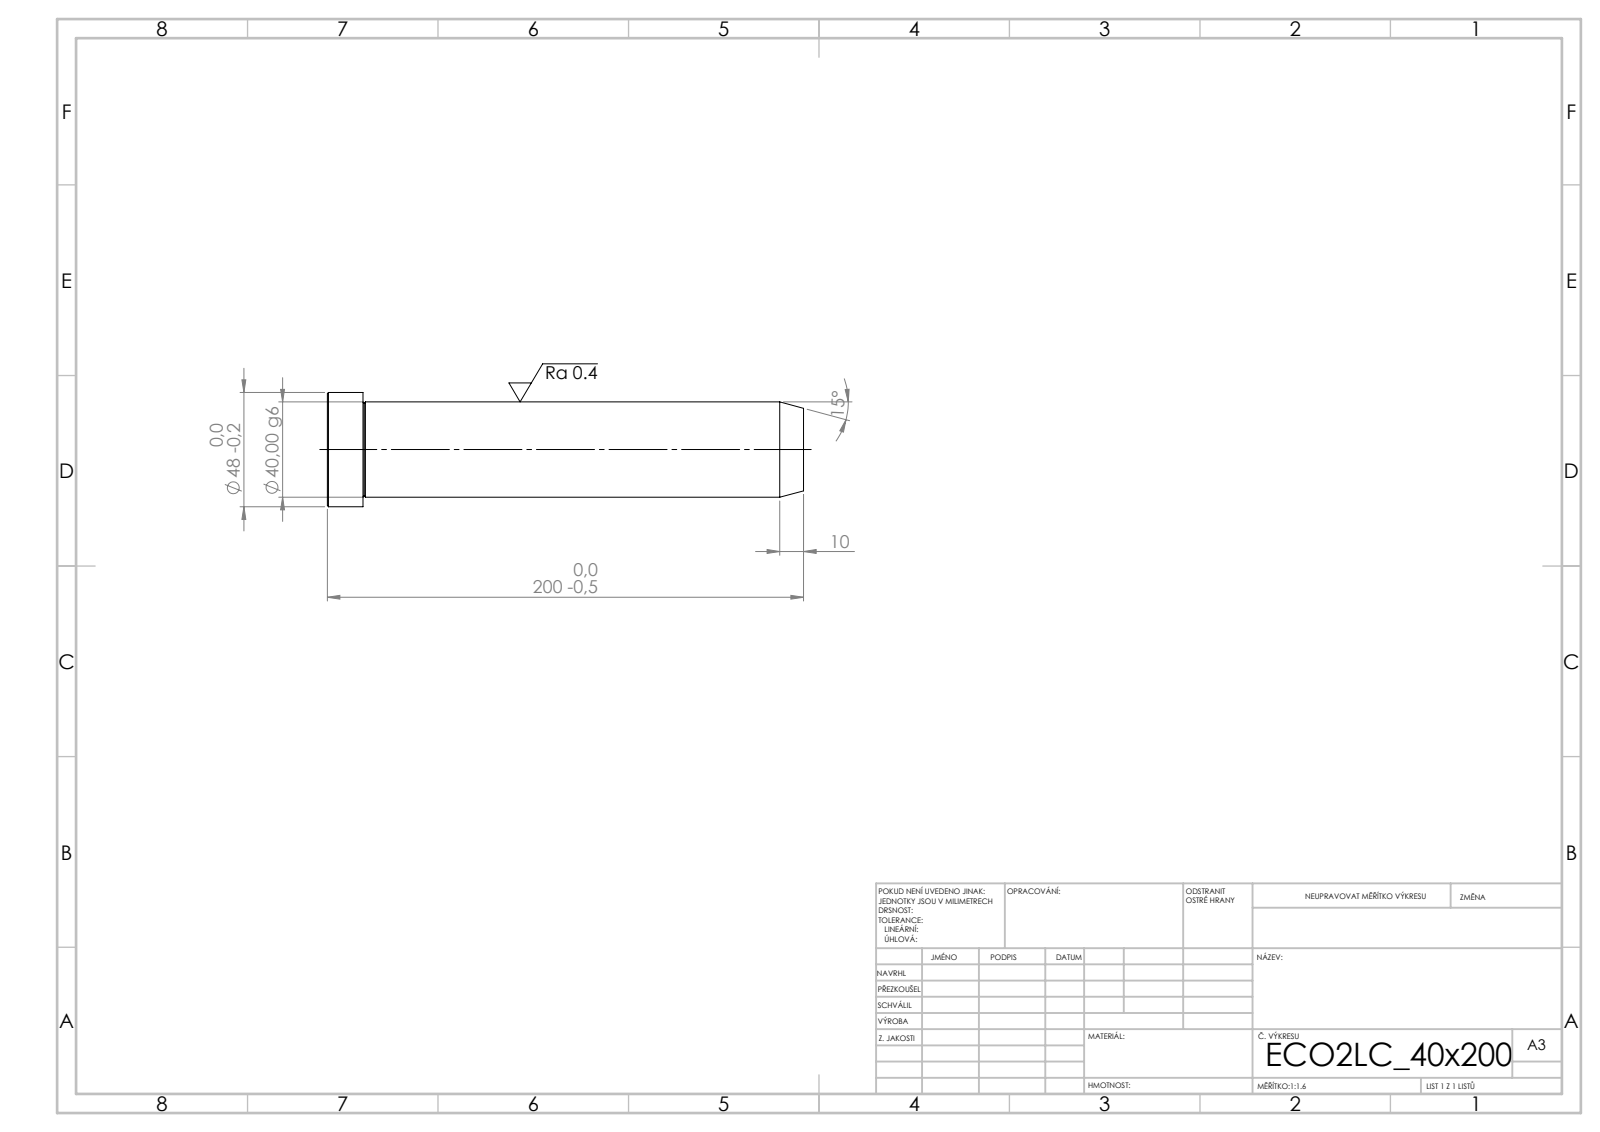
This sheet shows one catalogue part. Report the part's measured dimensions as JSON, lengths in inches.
{"step_written_by": "SolidWorks 2019 (CONFIG_CONTROL_DESIGN)", "units": "inches", "bodies": {"solids": 1, "faces": 15, "planar": 3, "cylindrical": 4, "other": 8}, "overall_size": [7.874, 1.89, 1.89], "volume_in3": 15.74, "surface_area_in2": 44.63, "round_bosses_or_shafts": [[1.89, 1], [1.575, 1]], "face_to_face_distances": [7.874, 7.283, 0.591]}
